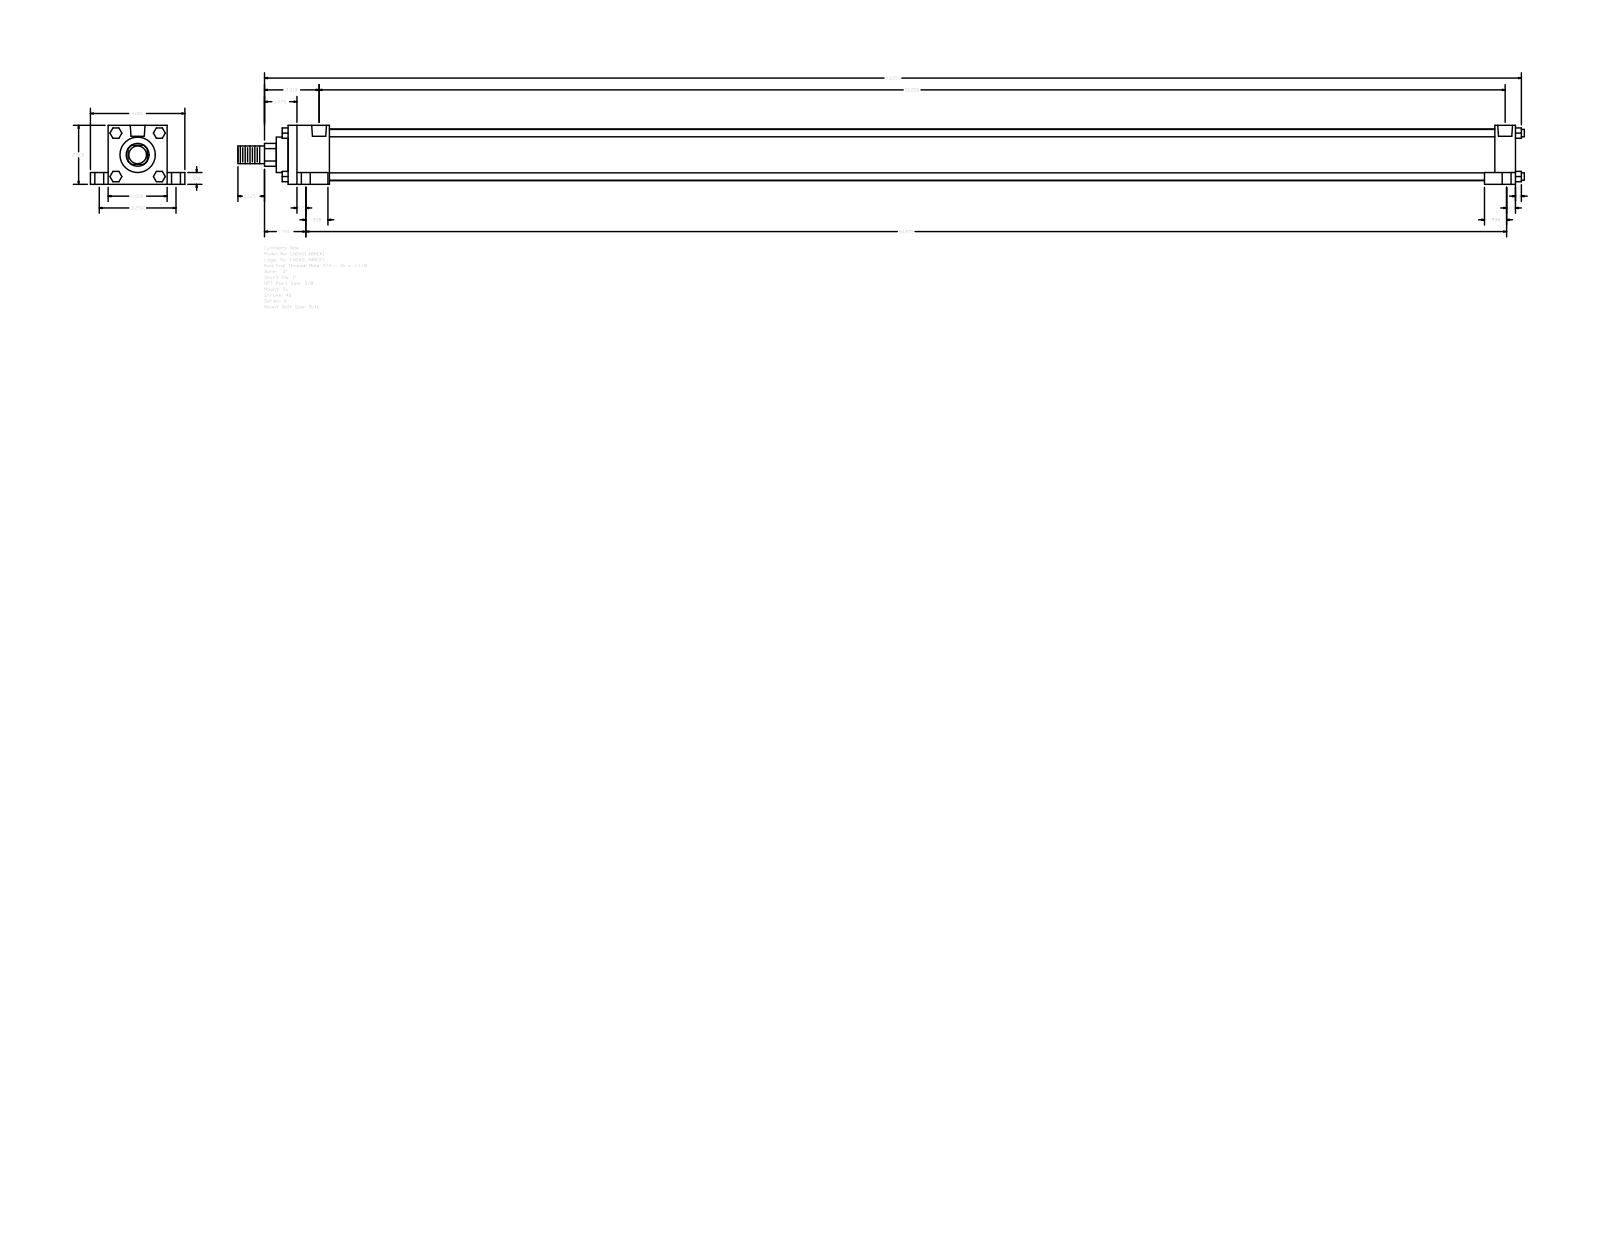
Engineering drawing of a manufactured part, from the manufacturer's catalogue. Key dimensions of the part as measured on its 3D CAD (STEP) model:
Part name (STEP PRODUCT): A_SL__0200_1
STEP written by: GSSL Pune (CONFIG_CONTROL_DESIGN)
Units: millimetres
Bodies: 0 solids, 148 faces (112 planar, 36 cylindrical, 0 other)
Overall size (bounding box): 1384.3 × 101.6 × 63.5
Round holes (diameter × count): ⌀5.56 ×4, ⌀9.53 ×4, ⌀15.88 ×4, ⌀15.93 ×2
Round bosses / shafts (diameter × count): ⌀7.94 ×4, ⌀55.63 ×1, ⌀38.1 ×1, ⌀25.4 ×1, ⌀19.05 ×1
Partial cylindrical surfaces — rounded edges, fillets, slot ends (radius × count): R12.29 ×1
Main face-to-face distances: 63.5, 1320.8, 12.7, 50.8, 19.05, 82.55, 44.45, 1276.35, 1298.57, 1254.12
Hole centre spacings: 41.3, 41.64, 43.67, 44.22, 82.54, 1270.78, 1277.01, 1278.6
